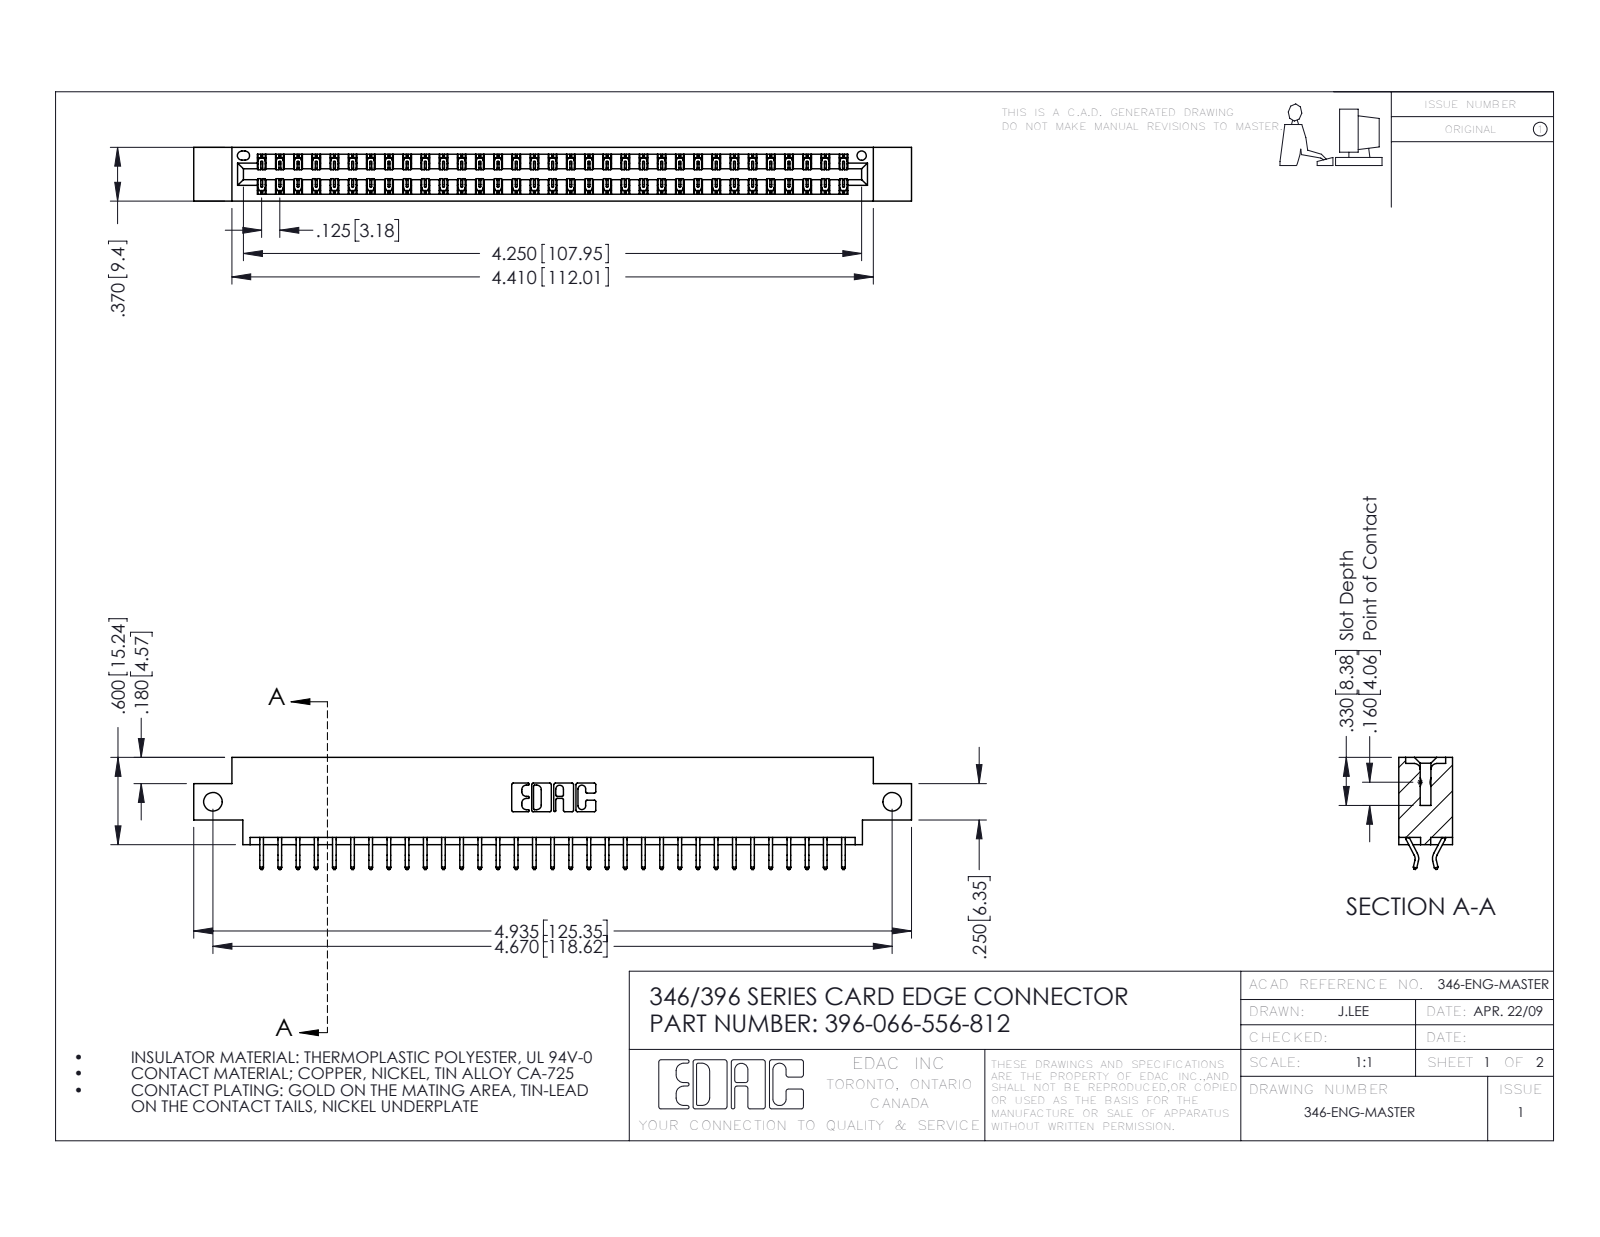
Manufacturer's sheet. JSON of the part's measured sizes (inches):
{"part_name": "345-292-001_556 Tail; 346 Part_0.170 Offset - Side Mount; 396-066-556-812", "step_written_by": "SolidWorks 2016 (CONFIG_CONTROL_DESIGN)", "units": "inches", "bodies": {"solids": 67, "faces": 3954, "planar": 2654, "cylindrical": 1300, "other": 0}, "overall_size": [4.935, 0.77, 0.37], "volume_in3": 0.727, "surface_area_in2": 25.12, "round_holes": [[0.128, 2], [0.064, 1]], "partial_cylinders_radius": [[0.006, 99], [0.01, 22], [0.007, 6], [0.031, 6], [0.026, 3], [0.01, 2], [0.014, 2], [0.022, 2]], "face_to_face_distances": [0.048, 0.322, 0.37, 0.25, 0.025, 0.072, 0.298, 0.275, 0.148, 0.222], "hole_center_spacings": [4.67]}
